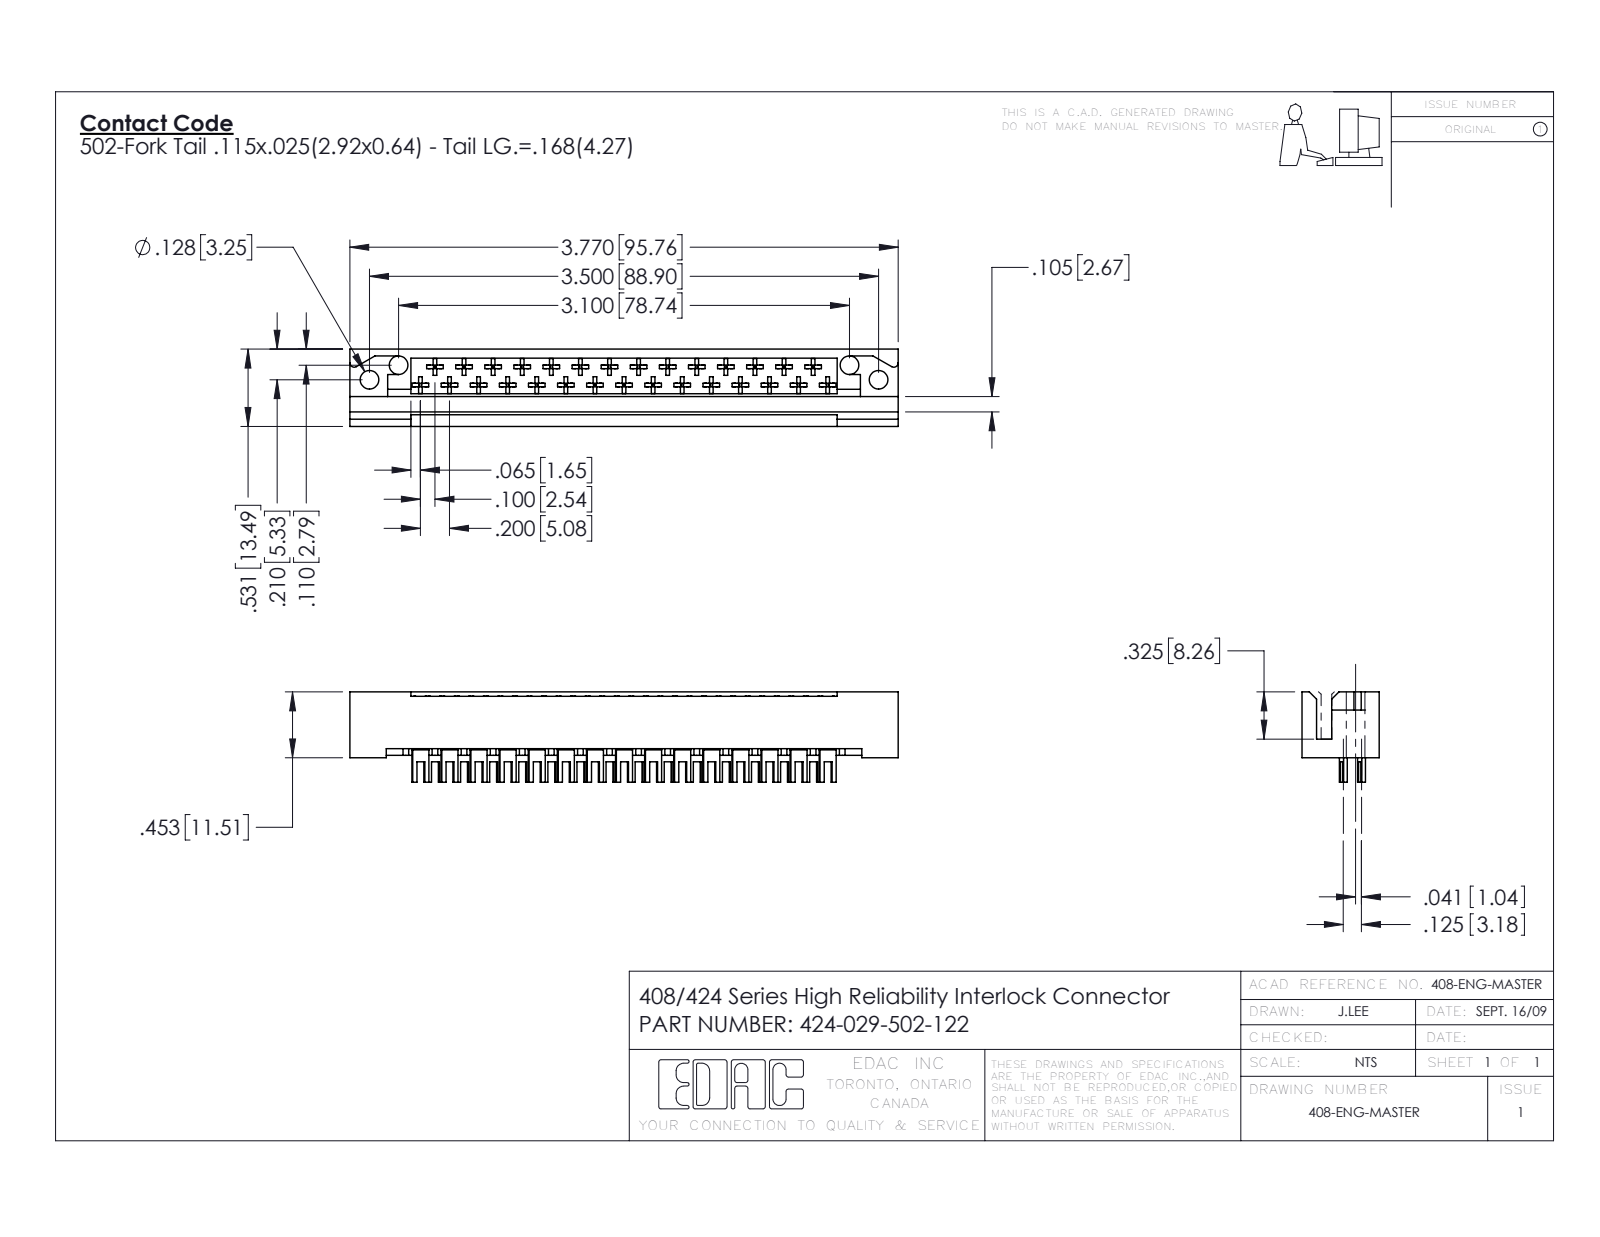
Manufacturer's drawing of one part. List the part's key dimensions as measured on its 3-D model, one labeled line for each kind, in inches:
Part name (STEP PRODUCT): 424 Part_029; 424-029-502-122; 408-290-001_408-290-102
STEP written by: SolidWorks 2016 (CONFIG_CONTROL_DESIGN)
Units: inches
Bodies: 30 solids, 1599 faces (1235 planar, 248 cylindrical, 116 other)
Overall size (bounding box): 3.77 × 0.621 × 0.531
Volume: 0.607 in³ · Surface area: 20.22 in²
Round holes (diameter × count): ⌀0.128 ×4
Partial cylindrical surfaces — rounded edges, fillets, slot ends (radius × count): R0.01 ×174, R0.02 ×31, R0.03 ×2
Main face-to-face distances: 0.1, 0.296, 0.531, 0.025, 0.125, 0.431, 0.259, 0.172, 0.272, 0.235
Hole centre spacings: 0.224, 3.302, 3.1, 3.5
